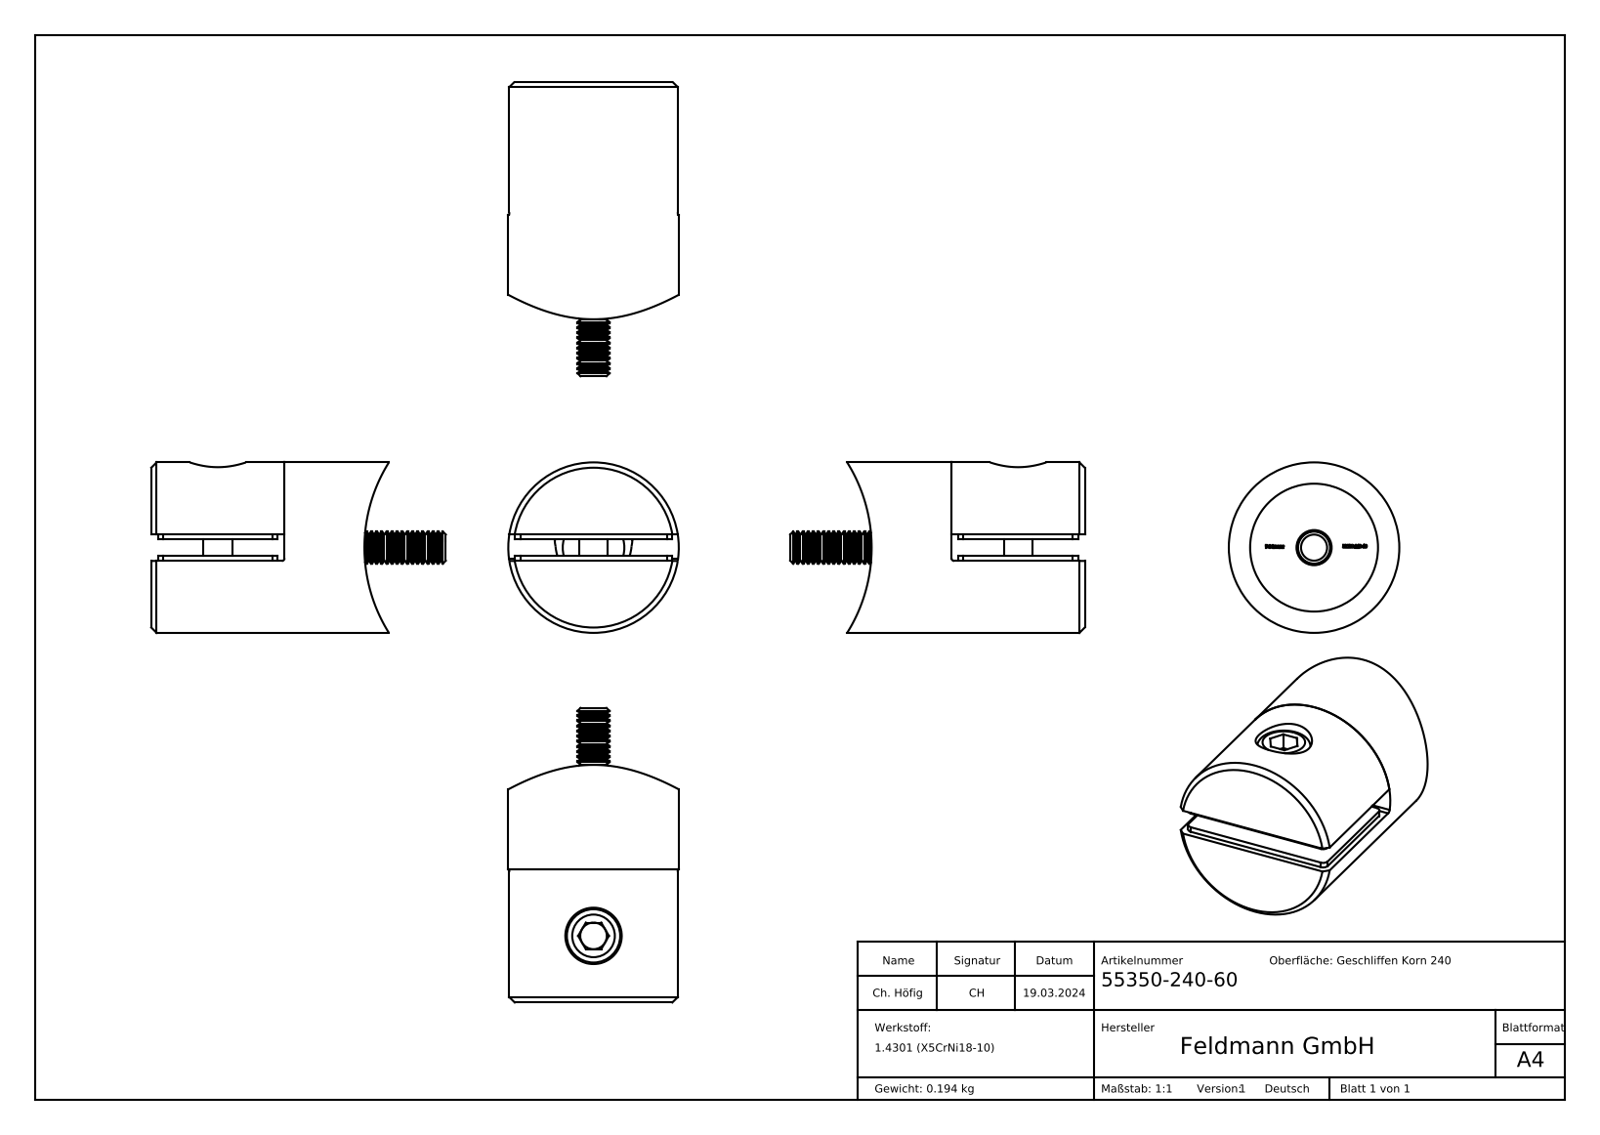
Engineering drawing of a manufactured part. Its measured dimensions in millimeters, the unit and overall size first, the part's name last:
Units: millimetres
Overall size (bounding box): 55.28 × 32 × 32
Round holes (diameter × count): ⌀4 ×2, ⌀5 ×1, ⌀6.5 ×1, ⌀6.6 ×1, ⌀7 ×1, ⌀10.58 ×1, ⌀24 ×1
Round bosses / shafts (diameter × count): ⌀4 ×2, ⌀32 ×1, ⌀11.57 ×1, ⌀10 ×1, ⌀6 ×1, ⌀5.35 ×1
Partial cylindrical surfaces — rounded edges, fillets, slot ends (radius × count): R1 ×4, R0.5 ×1, R7.15 ×1, R7.3 ×1, R30.15 ×1
Main face-to-face distances: 4, 1, 5, 3, 25, 9.5, 34.5, 7.5, 10.5, 6.5
Hole centre spacings: 9.55, 13
Volume: 26 478 mm³ · Surface area: 13 705 mm²
Bodies: 6 solids, 432 faces (192 planar, 55 cylindrical, 185 other)
Part name (STEP PRODUCT): 55350-240-60; socket countersunk head screw_din_DIN 7991 - M6 x 25 --- 25S; 5533X-240 Teil1_55350-240-60 Teil1; DIN 912 M6x18_DIN 912 M6x18 (+2 more)
STEP written by: SolidWorks 2018 (CONFIG_CONTROL_DESIGN)
